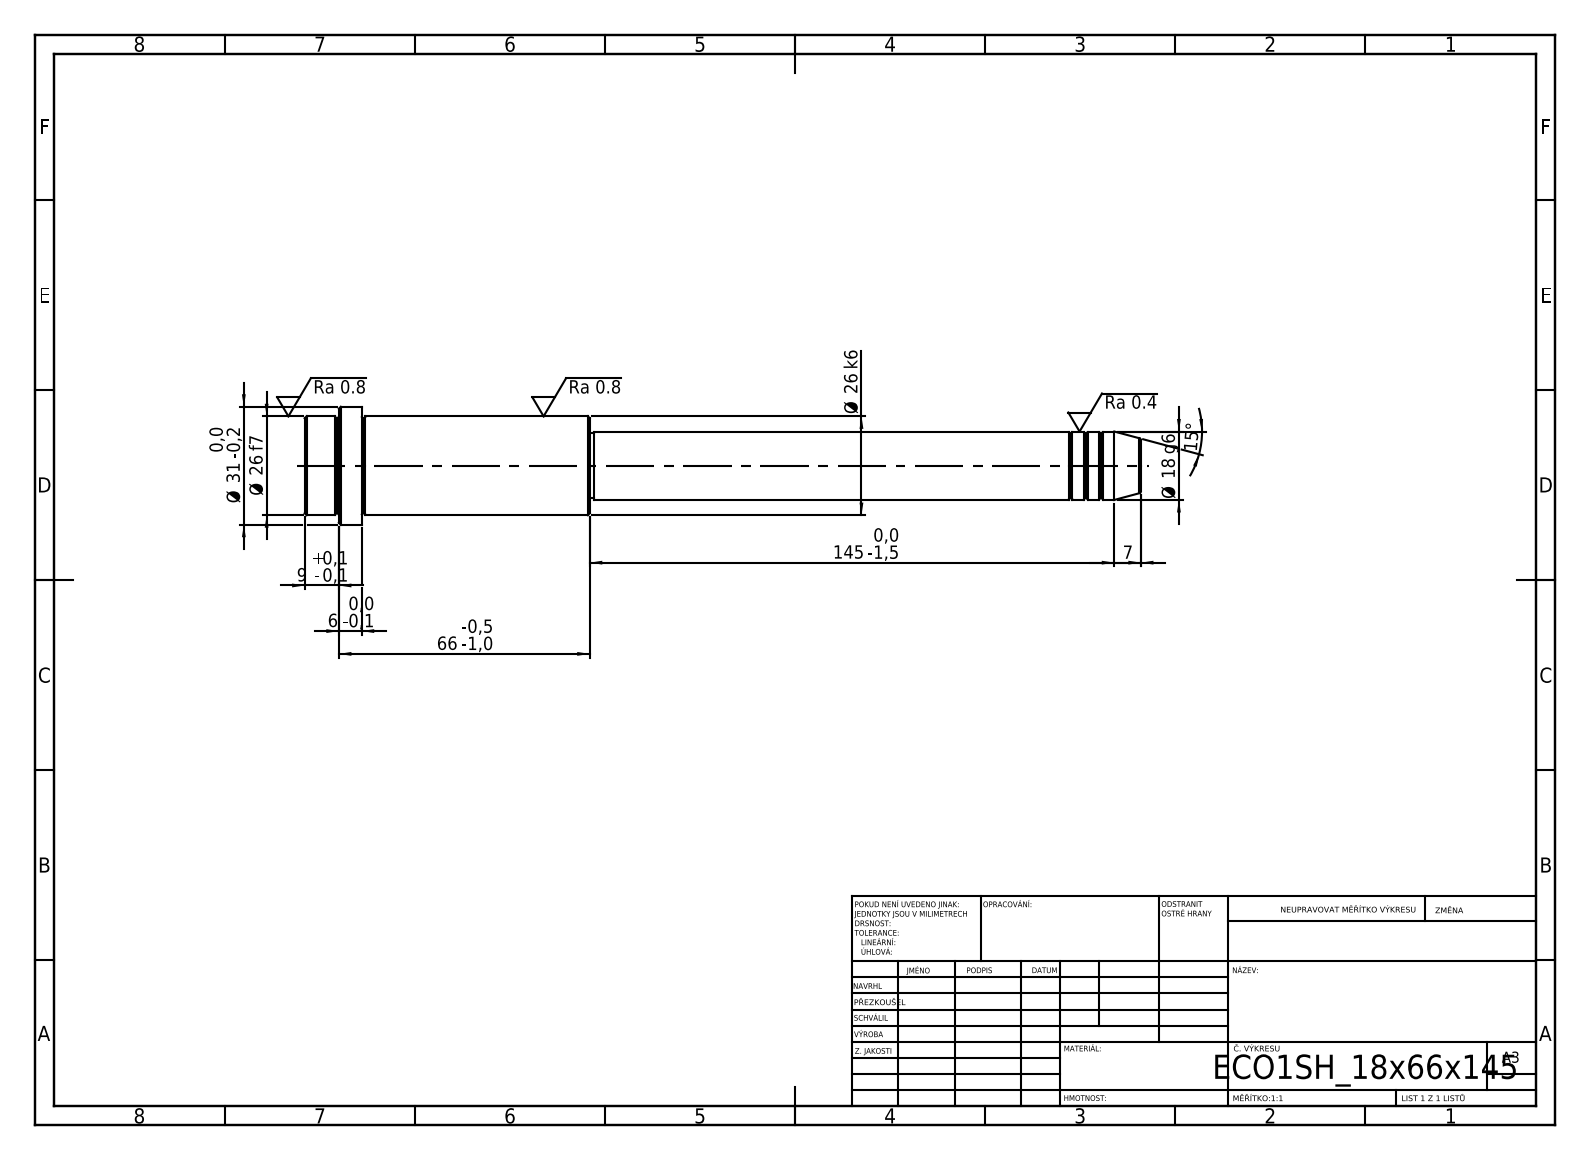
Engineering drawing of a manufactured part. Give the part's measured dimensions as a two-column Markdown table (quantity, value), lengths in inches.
| quantity | value |
| --- | --- |
| STEP written by | SolidWorks 2019 (CONFIG_CONTROL_DESIGN) |
| units | inches |
| bodies | 1 solid, 52 faces (6 planar, 16 cylindrical, 30 other) |
| overall size | 8.661 × 1.22 × 1.22 |
| volume | 4.731 in³ |
| surface area | 24.72 in² |
| round bosses / shafts (diameter × count) | 1.22 × 1, 1.024 × 1, 0.709 × 1, 0.669 × 1 |
| main face-to-face distances | 2.953, 2.362, 0.591, 2.598, 0.236, 0.354, 5.709, 8.071, 8.307, 8.661 |
